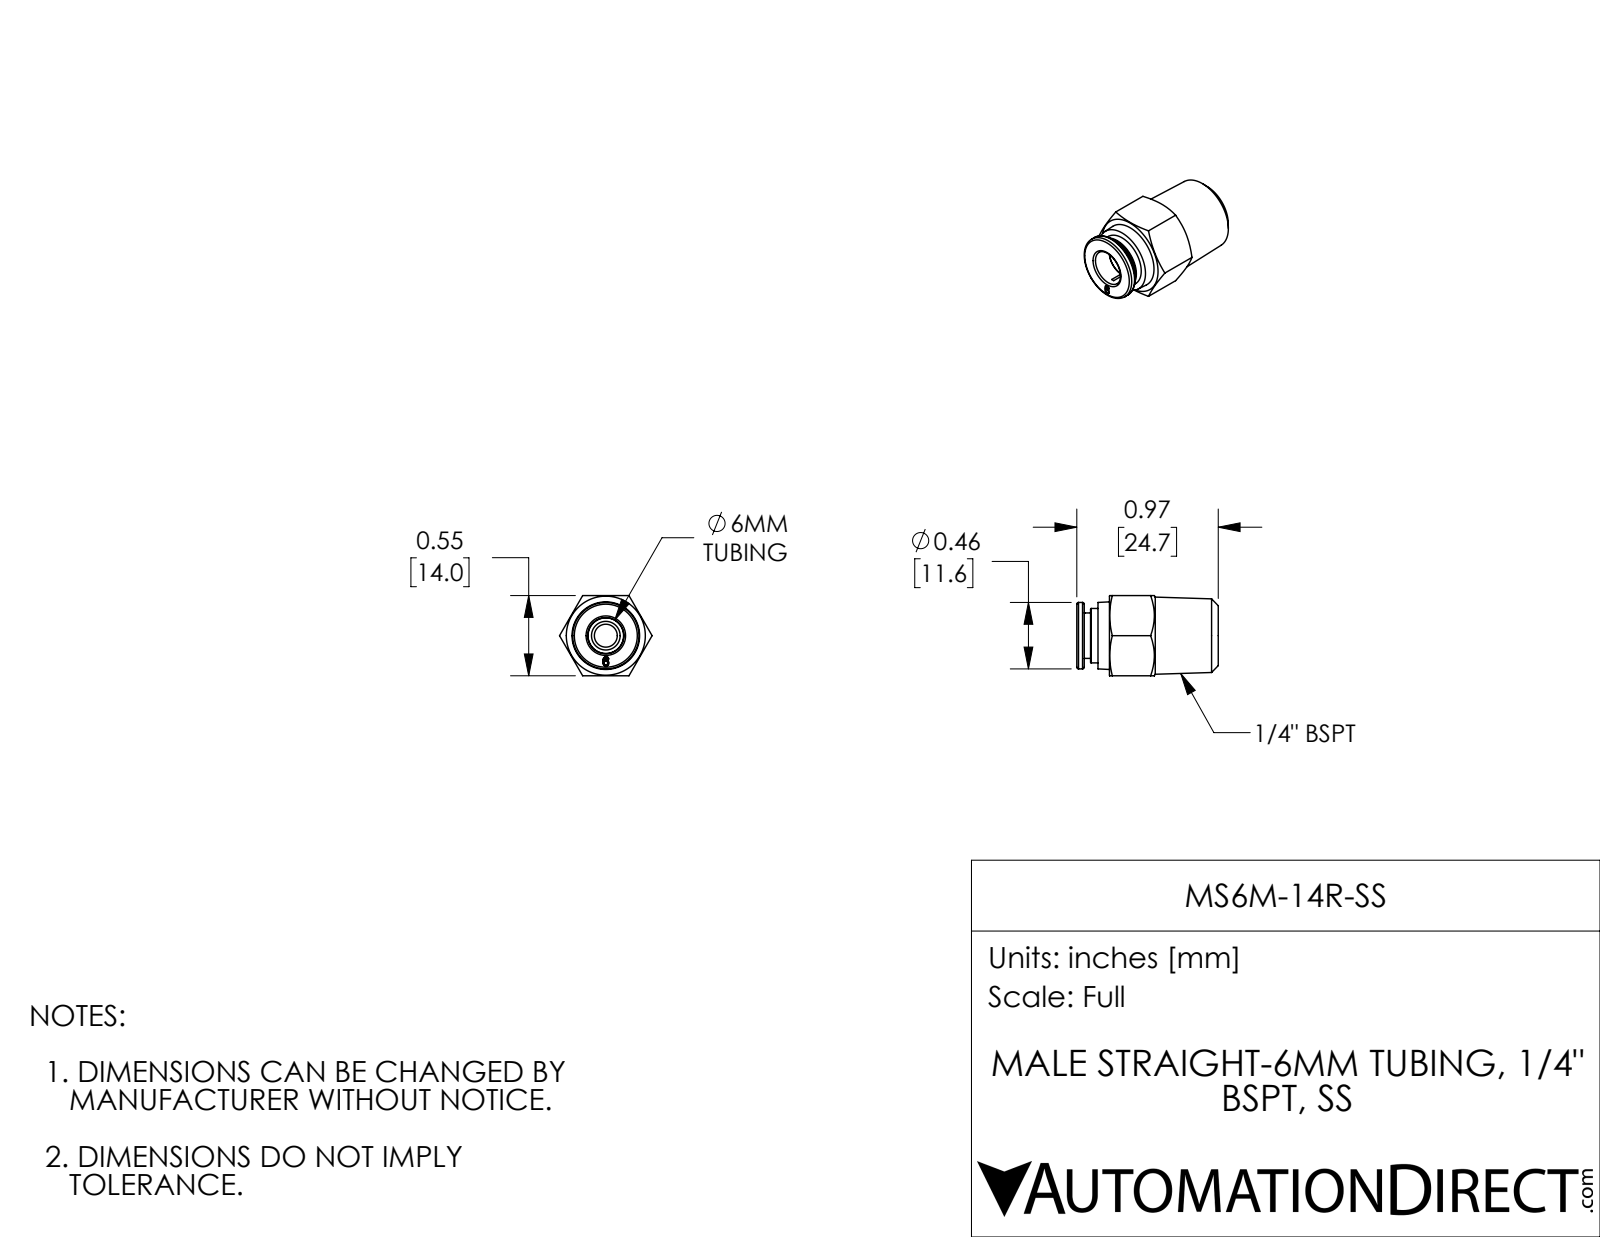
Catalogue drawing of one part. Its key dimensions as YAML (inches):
part_name: "MS6M-14R-SS"
step_written_by: "SolidWorks 2017 (AUTOMOTIVE_DESIGN)"
units: inches
bodies: {solids: 1, faces: 77, planar: 23, cylindrical: 14, other: 40}
overall_size: [0.972, 0.636, 0.551]
volume: 0.164
surface_area: 2.883
round_holes:
  - {diameter: 0.157, count: 1}
  - {diameter: 0.244, count: 1}
  - {diameter: 0.248, count: 1}
  - {diameter: 0.319, count: 1}
round_bosses_or_shafts:
  - {diameter: 0.457, count: 1}
  - {diameter: 0.374, count: 1}
  - {diameter: 0.313, count: 1}
face_to_face_distances: [0.551, 0.972, 0.051, 0.094, 0.921, 0.748, 0.173, 0.224, 0.827, 0.079]
